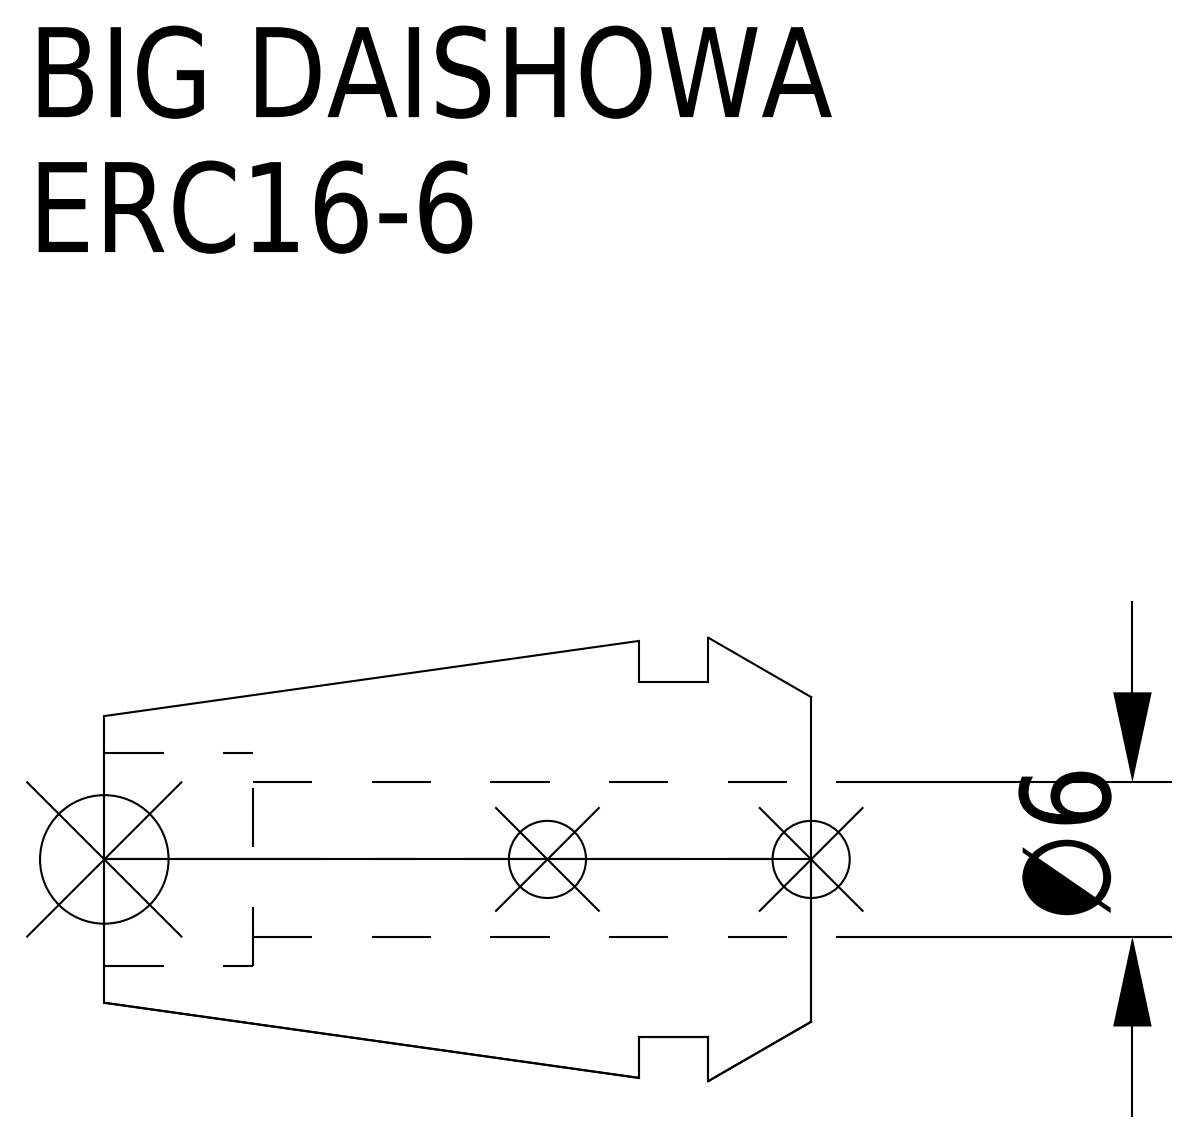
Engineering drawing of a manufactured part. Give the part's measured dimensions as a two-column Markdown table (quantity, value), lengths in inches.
| quantity | value |
| --- | --- |
| part name | ERC16-6 |
| STEP written by | CREO PARAMETRIC BY PTC INC, 2016380 (AUTOMOTIVE_DESIGN) |
| units | inches |
| bodies | 1 solid, 15 faces (5 planar, 6 cylindrical, 4 other) |
| overall size | 1.083 × 0.679 × 0.679 |
| volume | 0.212 in³ |
| surface area | 3.334 in² |
| round holes (diameter × count) | 0.236 × 1, 0.327 × 1 |
| round bosses / shafts (diameter × count) | 0.543 × 1 |
| main face-to-face distances | 0.157, 0.264, 0.106, 1.083, 0.925, 0.819, 0.855, 0.698, 0.591, 0.228 |
